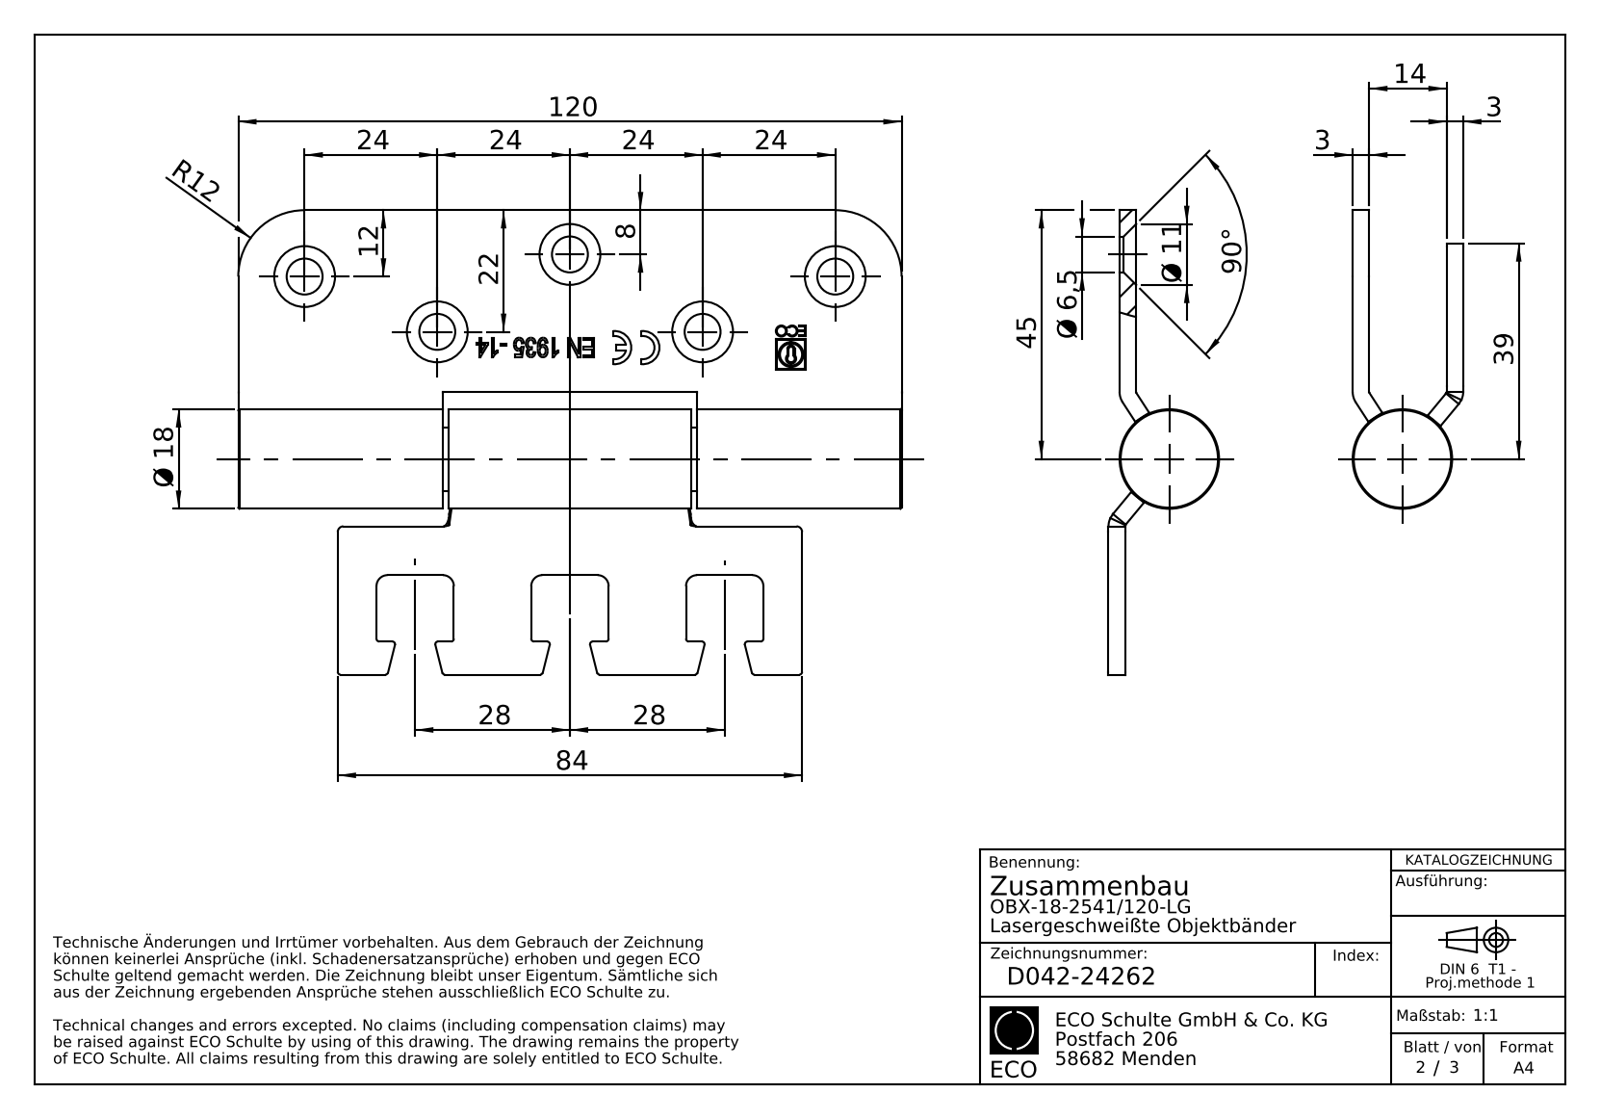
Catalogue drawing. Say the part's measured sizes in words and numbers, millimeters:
The part is named "OBX-18-2541-120-LG; D043-24264; DIN5401-III; D046-14312 (+4 more)". Its 3-D file was written by "SolidWorks 2017 (AUTOMOTIVE_DESIGN)". It is 11 solids with 400 faces: 220 planar, 95 cylindrical and 85 other. Overall it measures 120 by 54 by 20 millimeters. Its volume is 47 441 cubic millimeters and its surface area 28 657 square millimeters. Round holes: 5 of diameter 6.5, 2 of diameter 2, 1 of diameter 0.5, 1 of diameter 4.5, 1 of diameter 7.9. Round bosses or shafts: 1 of diameter 18, 1 of diameter 12, 1 of diameter 11.8, 1 of diameter 11.5, 1 of diameter 7.7, 1 of diameter 4, 1 of diameter 1.65. Partial cylindrical surfaces (rounded edges, fillets, slot ends): 22 of radius 0.5, 6 of radius 0.25, 6 of radius 2, 2 of radius 0.68, 2 of radius 1, 2 of radius 2.1, 2 of radius 3, 2 of radius 3.5. The main face-to-face distances are 3, 17, 20, 14, 82, 11.5, 108.5, 1, 120, 37. The hole center spacings are 26, 27.78, 48.17, 72.69, 1.95, 4.25, 4.6, 12.56.
